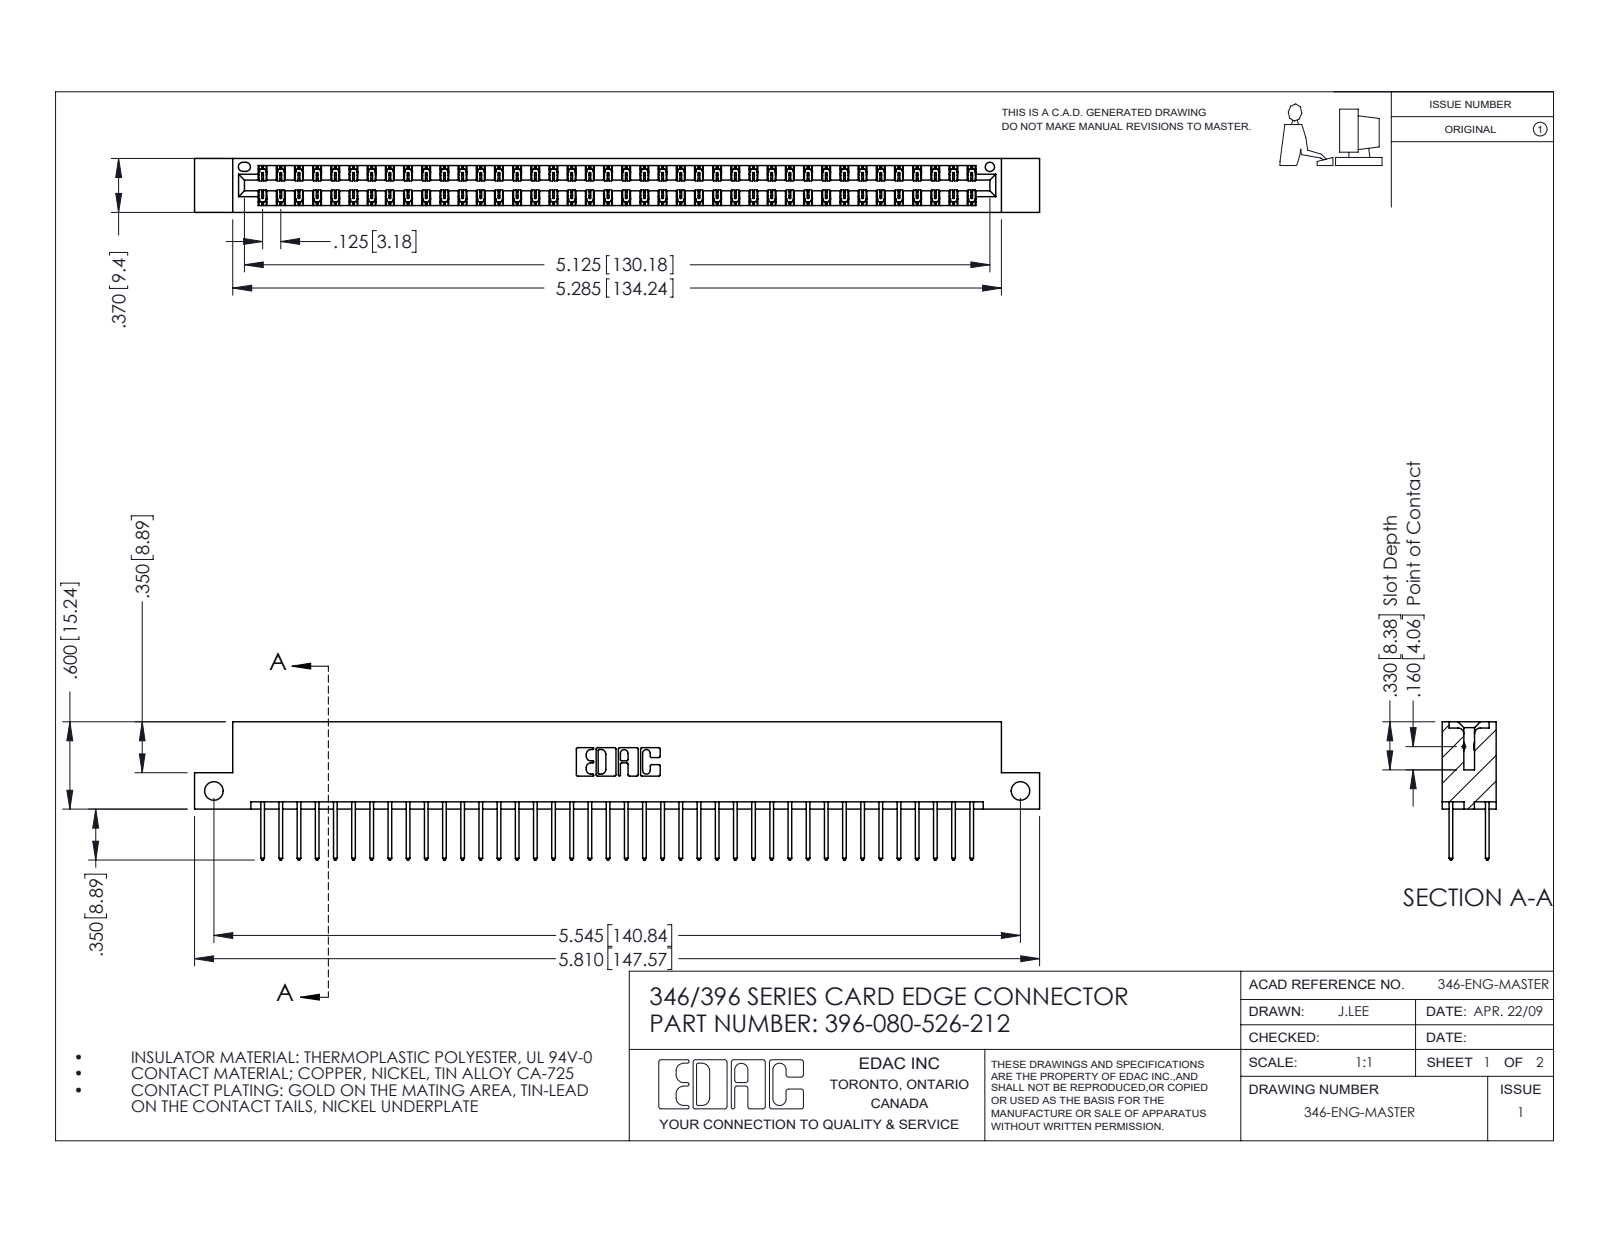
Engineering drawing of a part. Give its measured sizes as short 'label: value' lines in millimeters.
name: 396-080-526-212; 346 Part_Flush Mounting Lugs - Side Mount; 345-292-001_345-293-126
written by: SolidWorks 2016 (CONFIG_CONTROL_DESIGN)
unit: mm
bodies: 81 solids, 4282 faces (2876 planar, 1406 cylindrical, 0 other)
size: 147.6 × 24.1 × 9.4
volume: 14 400 mm³; area: 20 240 mm²
holes: 2× ⌀3.3, 1× ⌀1.6
rounds: 120× R0.2, 80× R0.3, 22× R0.3, 6× R0.2, 6× R0.8, 3× R0.7, 2× R0.4, 2× R0.6
face distances: 1.2, 8.2, 6.4, 9.4, 1.8, 7.6, 0.6, 7, 3.8, 5.6
hole spacings: 140.8
